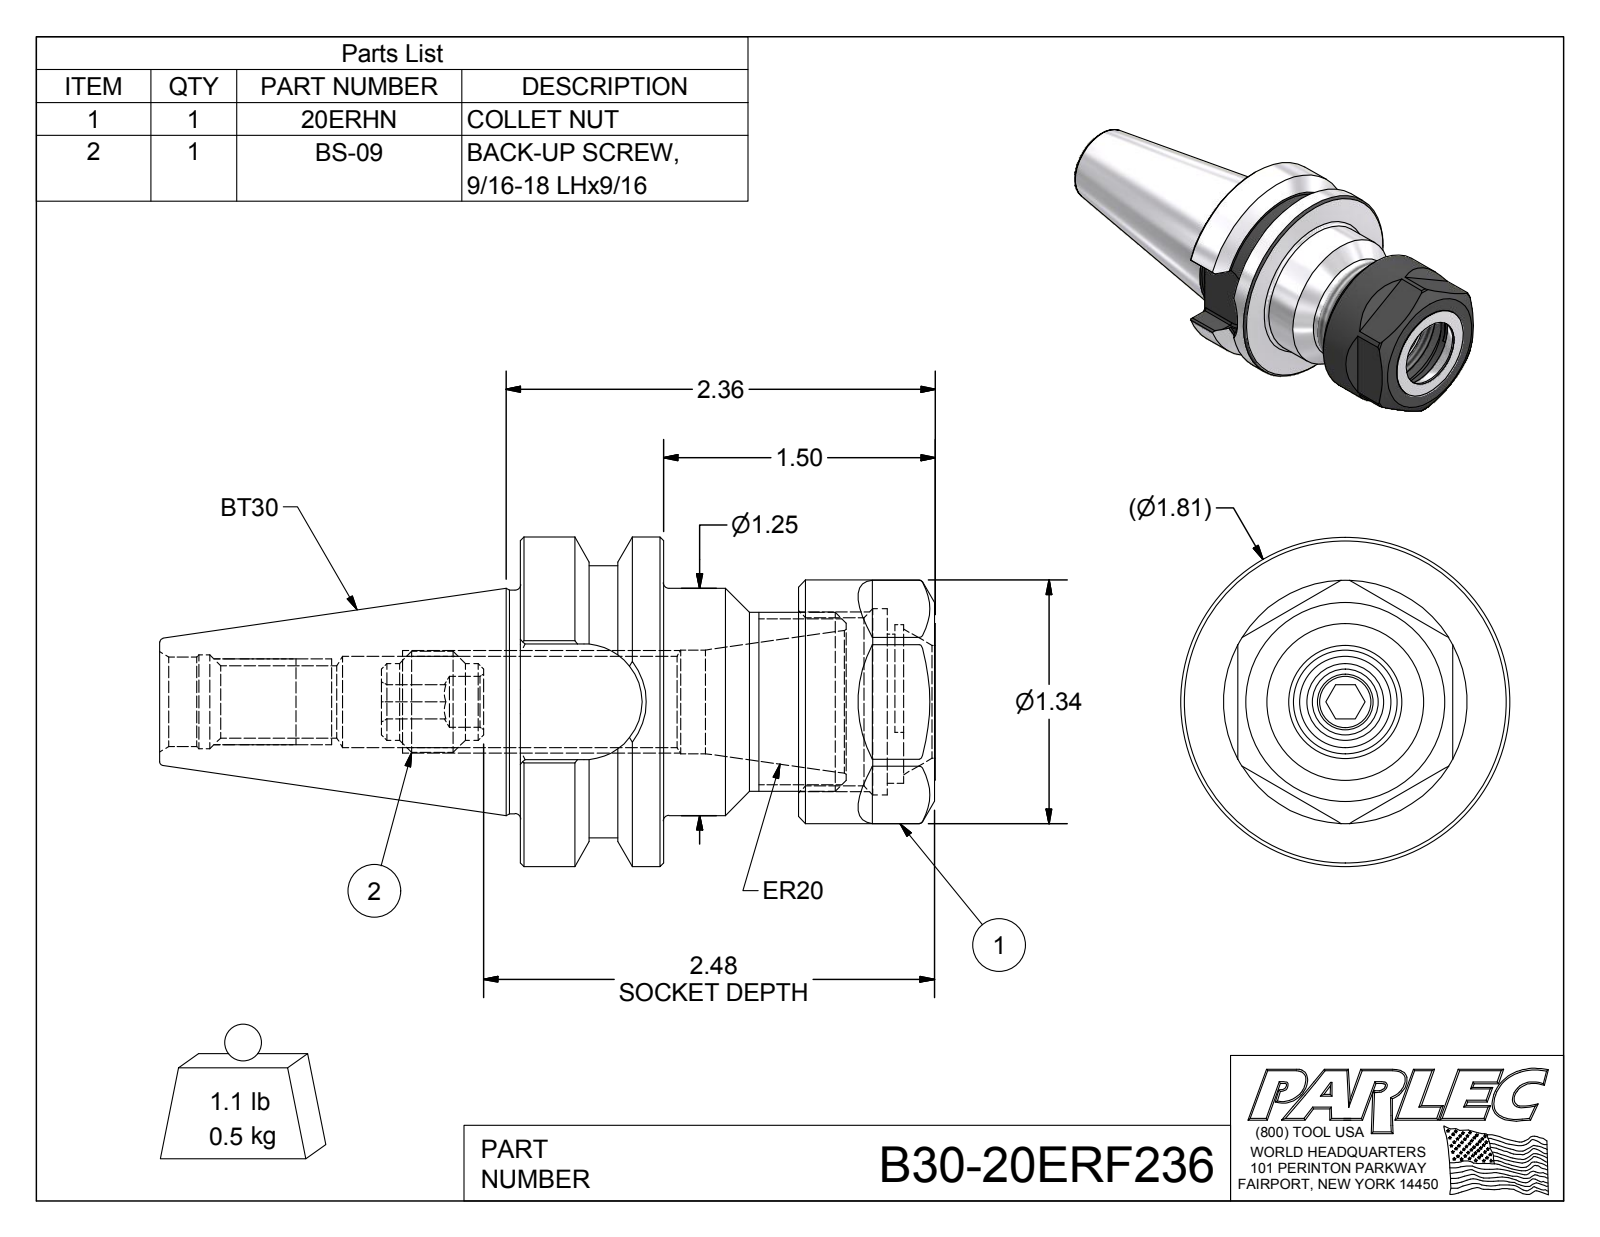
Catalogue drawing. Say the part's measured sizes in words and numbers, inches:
The part is named "B30-20ER236-1; BS-09; 20ERHN; B30-20ERF236". Its 3-D file was written by "Autodesk Inventor 2016 (AUTOMOTIVE_DESIGN)". It is 3 solids with 130 faces: 54 planar, 34 cylindrical and 42 other. Overall it measures 4.266 by 1.811 by 1.811 inches. Its volume is 3.939 cubic inches and its surface area 32.91 square inches. Round holes: 1 of diameter 0.281, 1 of diameter 0.398, 1 of diameter 0.493, 1 of diameter 0.502, 1 of diameter 0.517, 1 of diameter 0.57, 1 of diameter 0.61, 1 of diameter 0.925, 1 of diameter 1.024. Round bosses or shafts: 1 of diameter 1.811, 1 of diameter 1.339, 1 of diameter 1.25, 1 of diameter 1.23, 1 of diameter 0.984, 1 of diameter 0.555, 1 of diameter 0.422. Partial cylindrical surfaces (rounded edges, fillets, slot ends): 8 of radius 0.02, 1 of radius 0.319, 1 of radius 0.373, 1 of radius 0.415, 1 of radius 0.423, 1 of radius 0.748. The main face-to-face distances are 0.787, 2.282, 1.495, 1.181, 1.531, 0.744, 0.75, 0.051, 1.232, 1.283.
